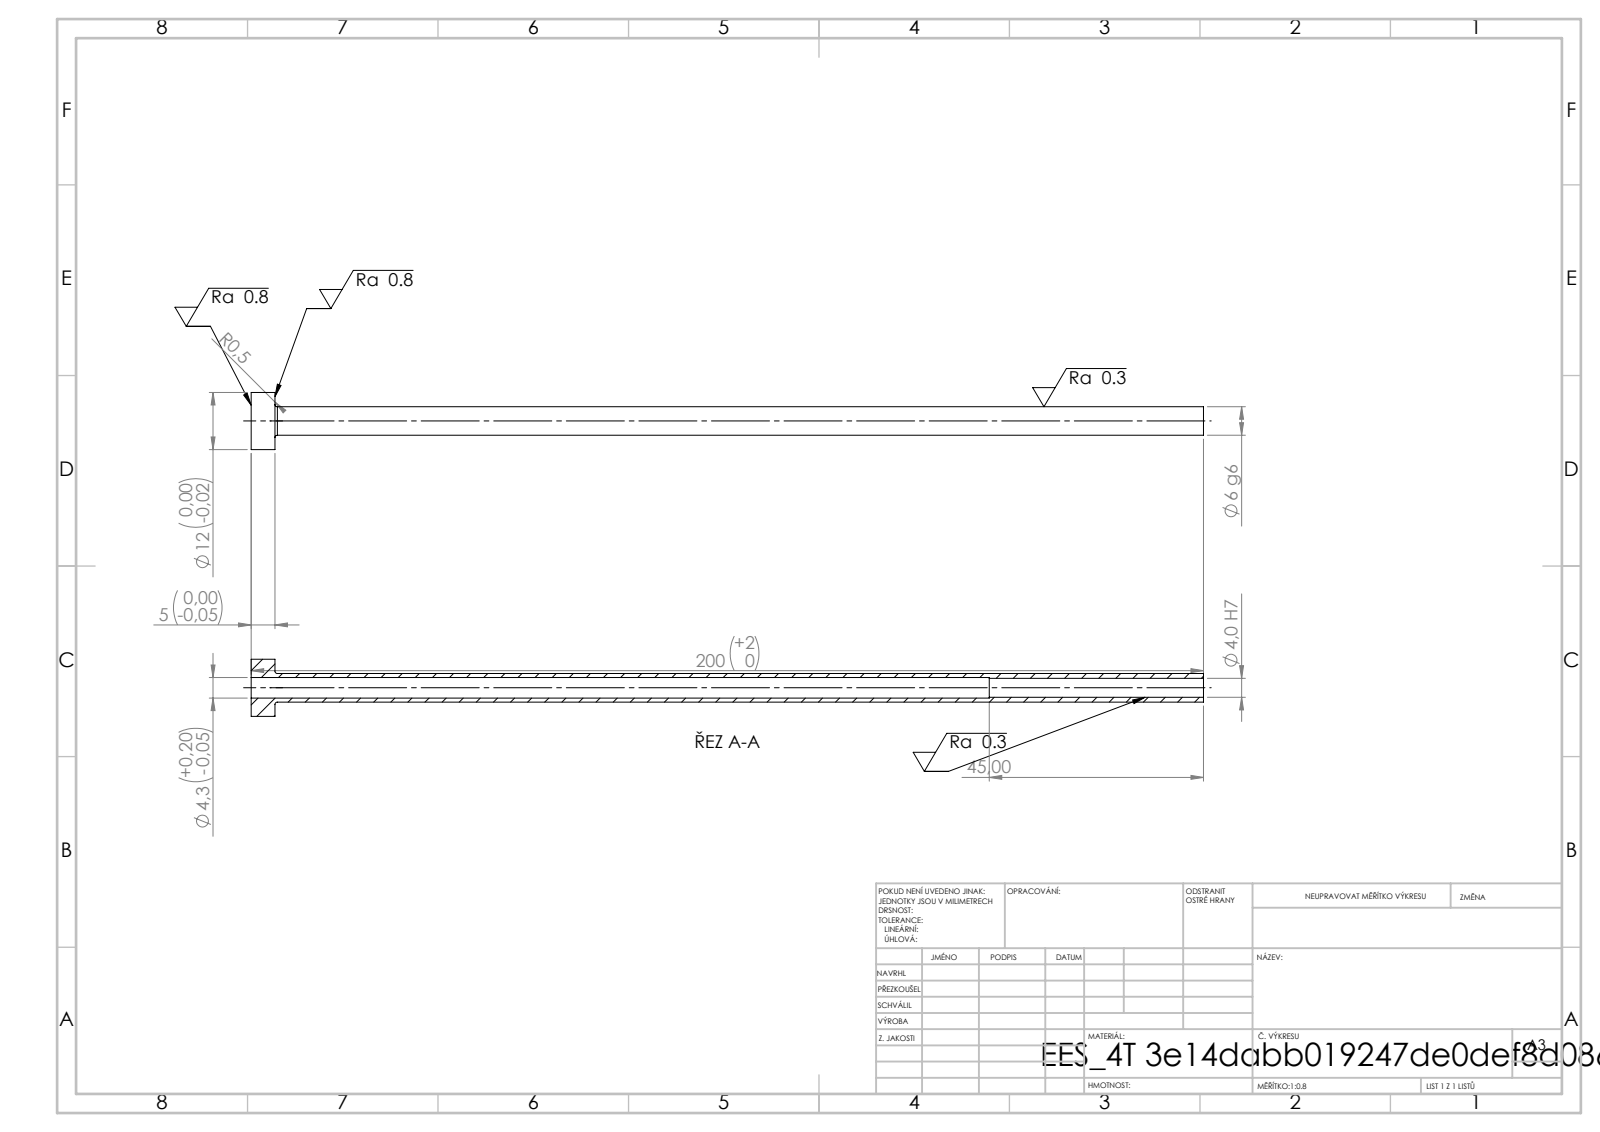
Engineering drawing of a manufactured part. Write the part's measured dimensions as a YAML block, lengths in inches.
step_written_by: "SolidWorks 2019 (CONFIG_CONTROL_DESIGN)"
units: inches
bodies: {solids: 1, faces: 14, planar: 4, cylindrical: 8, other: 2}
overall_size: [7.874, 0.472, 0.472]
volume: 0.199
surface_area: 10.42
round_holes:
  - {diameter: 0.157, count: 1}
  - {diameter: 0.169, count: 1}
round_bosses_or_shafts:
  - {diameter: 0.472, count: 1}
  - {diameter: 0.236, count: 1}
face_to_face_distances: [0.197, 7.874, 7.677, 6.102, 5.906, 1.772]
